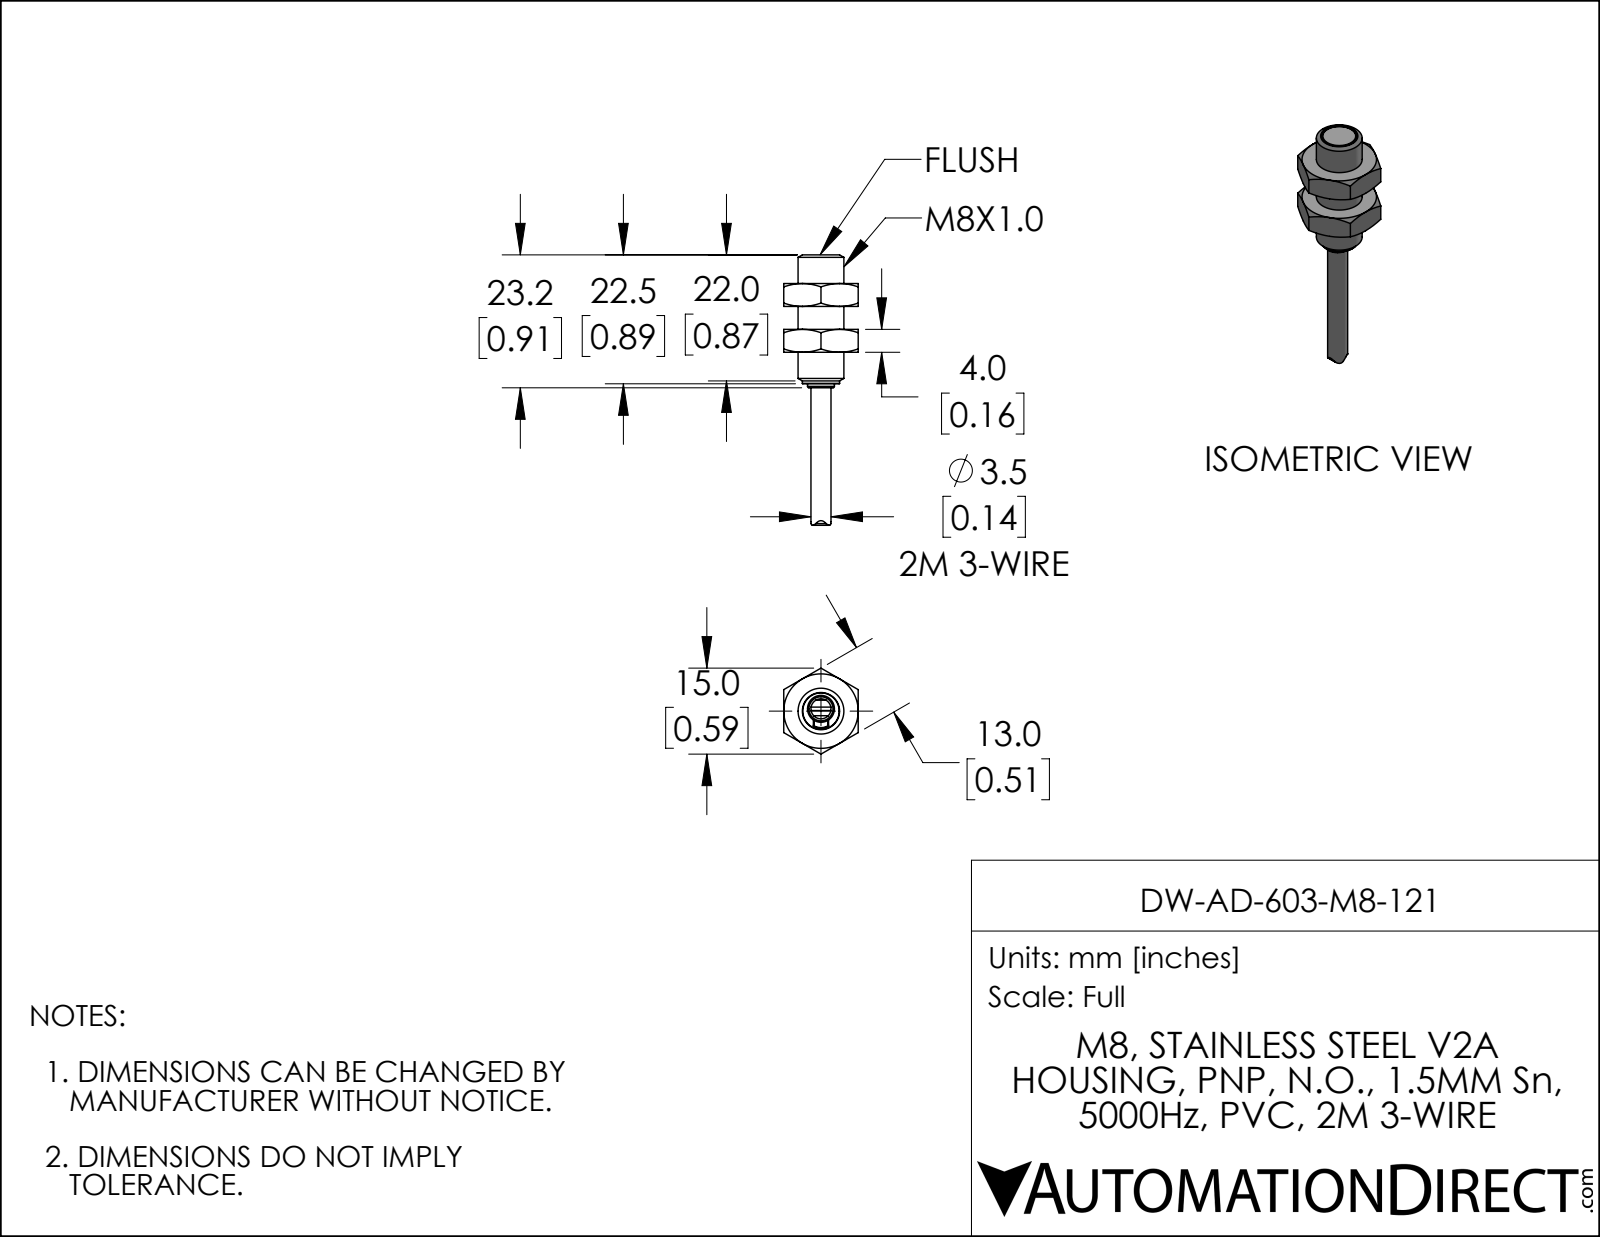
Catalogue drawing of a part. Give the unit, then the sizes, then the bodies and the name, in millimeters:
Units: millimetres
Overall size (bounding box): 47.2 × 15 × 13
Round bosses / shafts (diameter × count): ⌀8 ×1, ⌀6.5 ×1, ⌀4.7 ×1, ⌀3.5 ×1
Partial cylindrical surfaces — rounded edges, fillets, slot ends (radius × count): R0.3 ×2, R0.6 ×1, R0.8 ×1, R2.9 ×1, R3 ×1, R4.5 ×1, R6 ×1
Main face-to-face distances: 4, 13, 8, 12, 5, 9, 17, 22.5, 17.5, 13.5
Volume: 2 110 mm³ · Surface area: 1 435 mm²
Bodies: 1 solid, 79 faces (24 planar, 18 cylindrical, 37 other)
Part name (STEP PRODUCT): DW-AD-603-M8-121
STEP written by: SolidWorks 2019 (AUTOMOTIVE_DESIGN)
